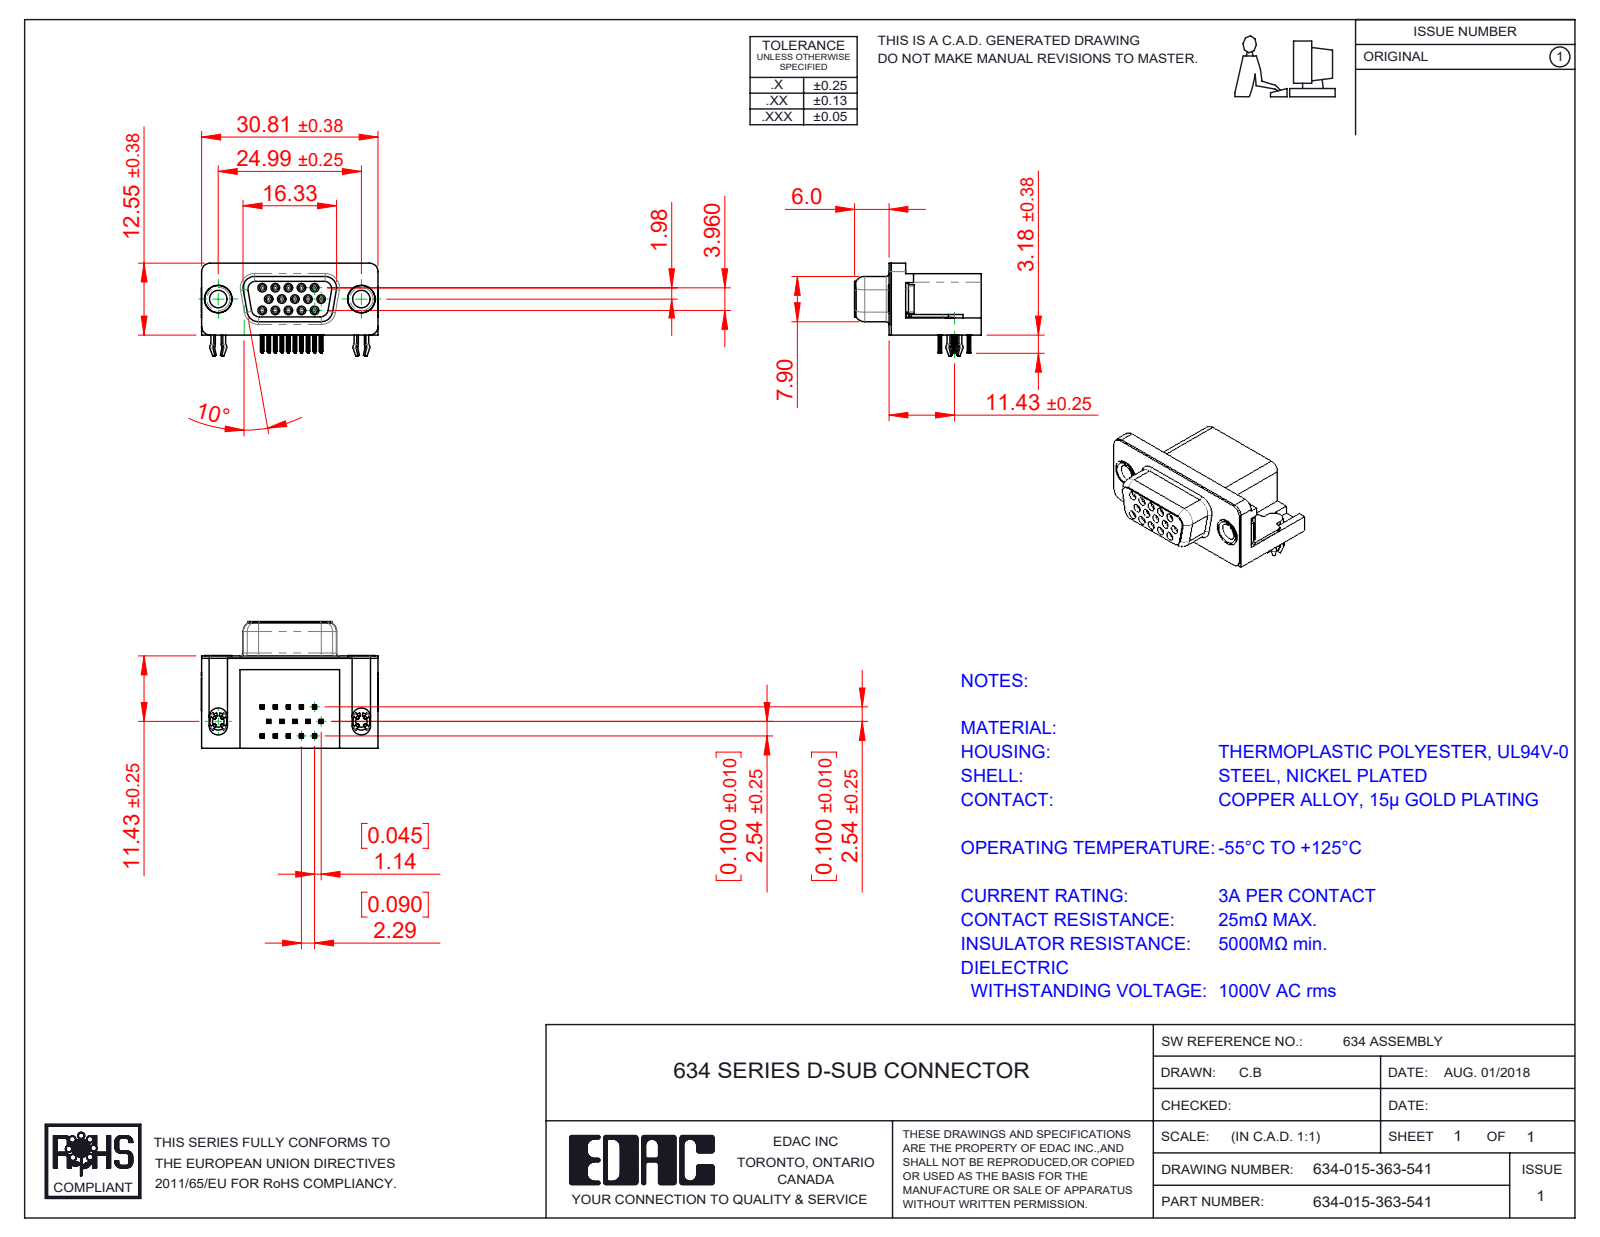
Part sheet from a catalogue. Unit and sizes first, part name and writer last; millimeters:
Units: millimetres
Overall size (bounding box): 30.89 × 22.1 × 16.25
Round holes (diameter × count): ⌀0.8 ×15, ⌀0.9 ×15, ⌀2 ×2, ⌀3.05 ×2, ⌀4 ×2, ⌀4.8 ×2, ⌀5 ×2
Round bosses / shafts (diameter × count): ⌀1.2 ×15, ⌀4.9 ×2, ⌀4.75 ×2, ⌀3.85 ×2, ⌀3 ×2
Partial cylindrical surfaces — rounded edges, fillets, slot ends (radius × count): R0.1 ×120, R0.15 ×60, R0.35 ×30, R1 ×19, R0.34 ×15, R0.25 ×12, R1.35 ×8, R1.6 ×8
Main face-to-face distances: 0.4, 10.35, 15.7, 16.1, 0.35, 2.5, 2.9, 6.4, 0.6, 10.7
Hole centre spacings: 2.29, 2.28, 3.96, 4.57, 6.05, 3.97, 4.58, 6.86
Volume: 4 551 mm³ · Surface area: 6 556 mm²
Bodies: 21 solids, 2501 faces (1108 planar, 587 cylindrical, 806 other)
Part name (STEP PRODUCT): Contact Bottom; Contact Top; 4 Prong Board Lock; Contact Middle (+4 more)
STEP written by: SolidWorks 2016 (CONFIG_CONTROL_DESIGN)
